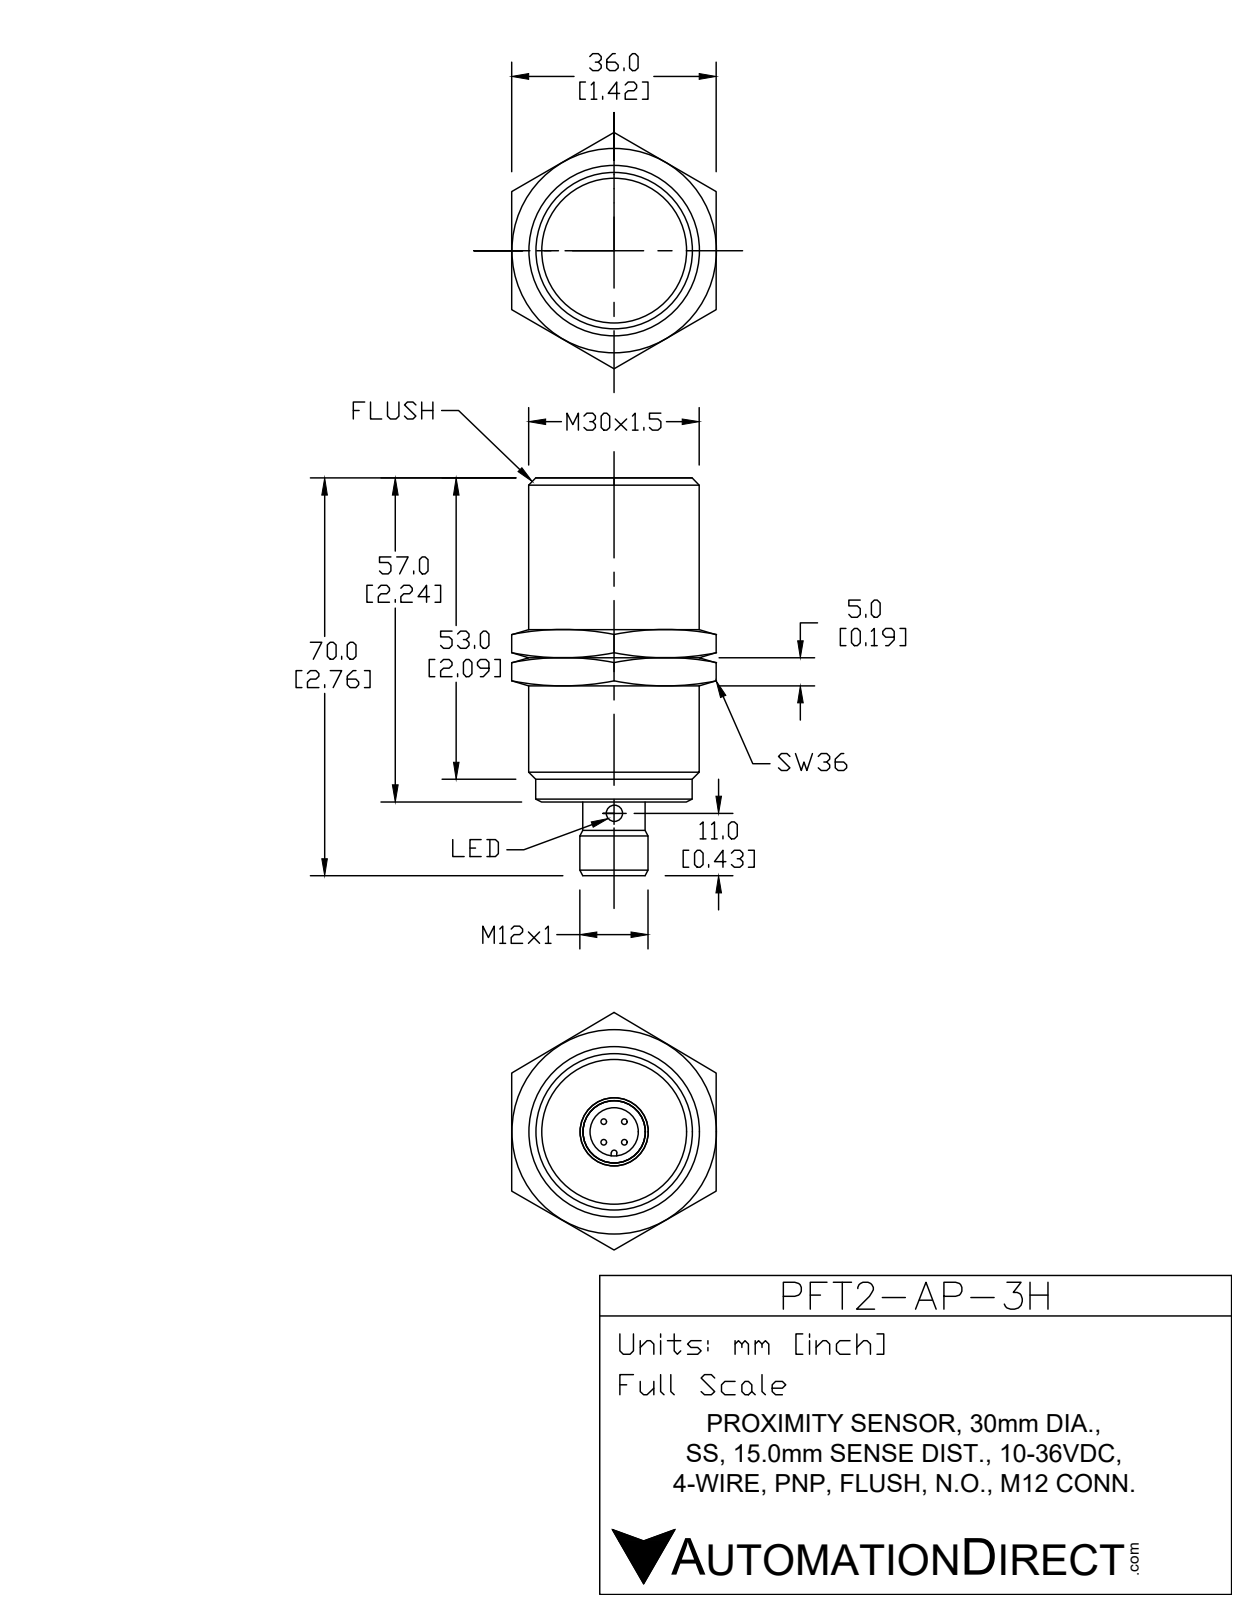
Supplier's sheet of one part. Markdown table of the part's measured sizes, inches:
| quantity | value |
| --- | --- |
| part name | PFT2-AP-3H |
| STEP written by | SolidWorks 2017 (AUTOMOTIVE_DESIGN) |
| units | inches |
| bodies | 3 solids, 112 faces (25 planar, 36 cylindrical, 51 other) |
| overall size | 2.756 × 1.637 × 1.417 |
| volume | 2.754 in³ |
| surface area | 17.29 in² |
| round holes (diameter × count) | 0.098 × 2, 0.331 × 1, 1.117 × 1 |
| round bosses / shafts (diameter × count) | 1.181 × 1, 1.094 × 1, 1.087 × 1, 1.083 × 1, 1.059 × 1, 0.472 × 1, 0.445 × 1, 0.417 × 1 |
| partial cylindrical surfaces (radius × count) | 0.024 × 1, 0.195 × 1 |
| main face-to-face distances | 0.197, 0.984, 1.417, 1.26, 2.244, 1.063, 1.181, 1.457, 0.394, 0.787 |
